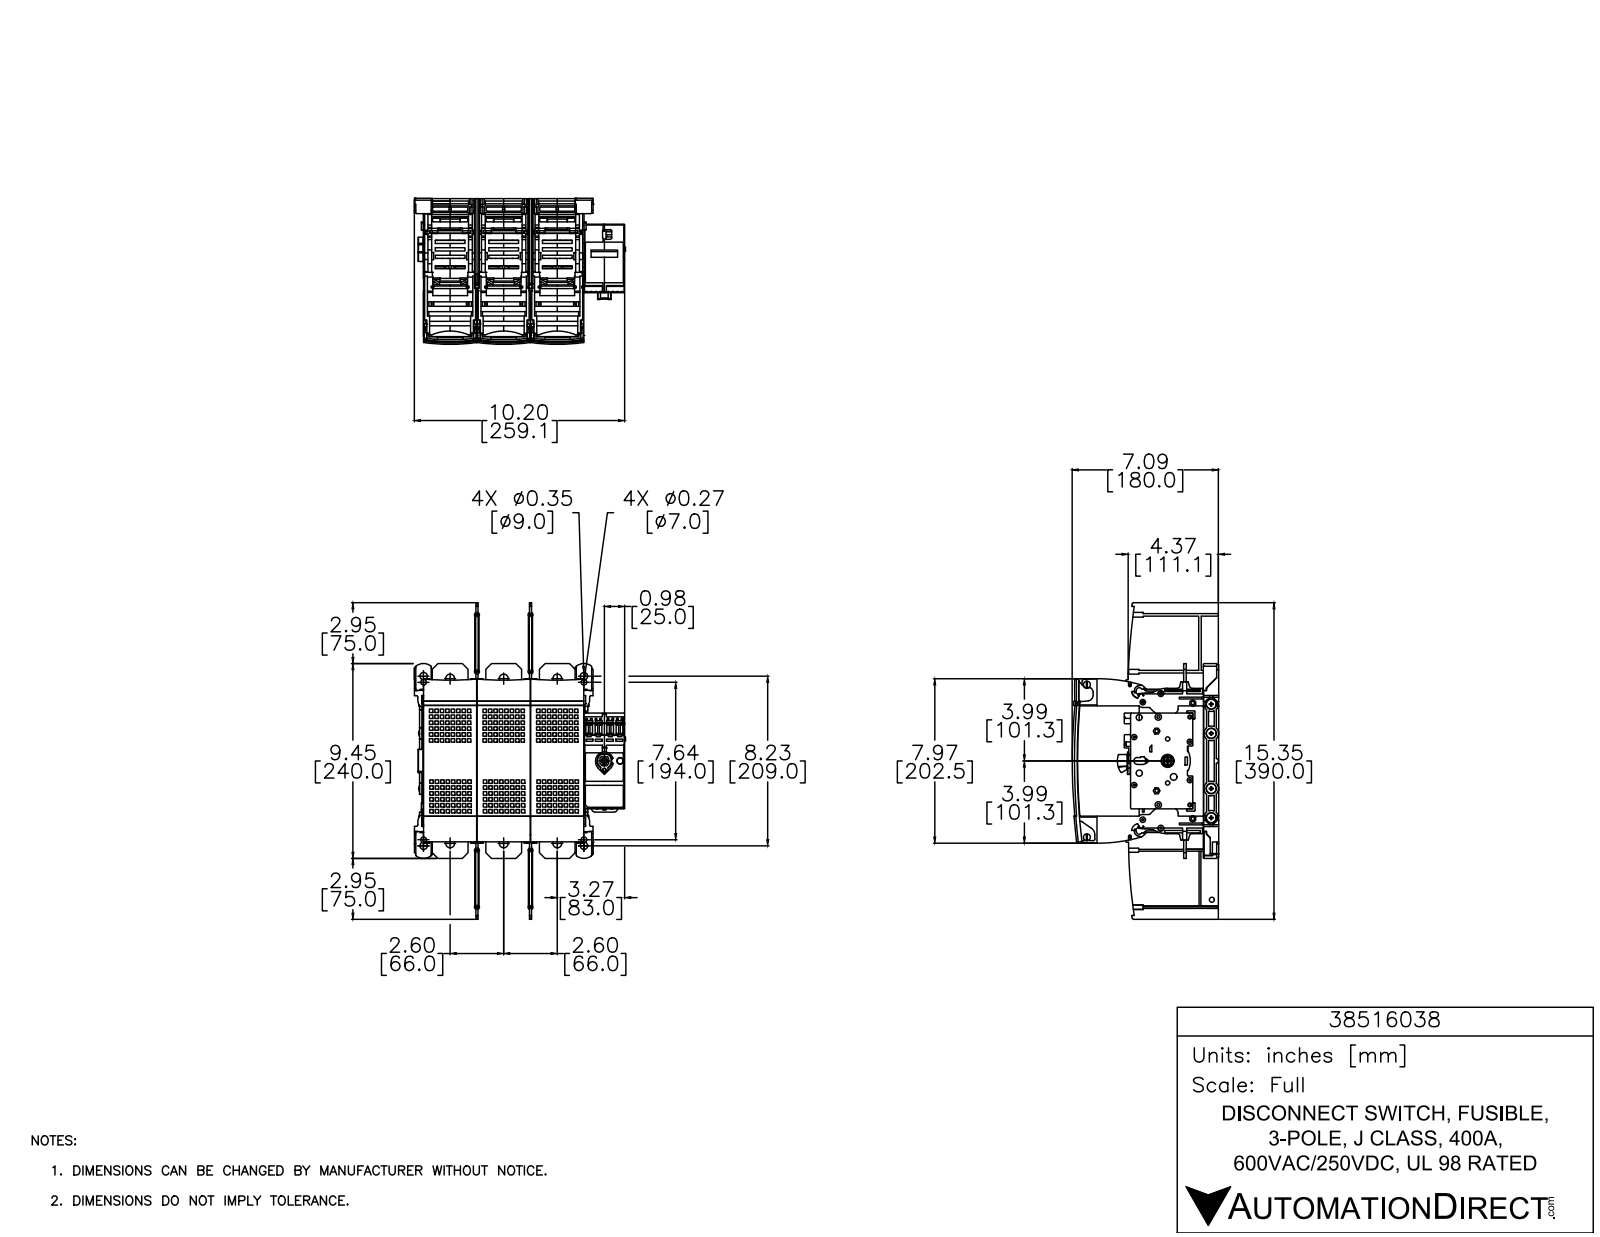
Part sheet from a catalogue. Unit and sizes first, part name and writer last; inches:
Units: inches
Overall size (bounding box): 15.354 × 10.217 × 7.087
Round holes (diameter × count): ⌀0.433 ×6, ⌀0.1 ×4, ⌀0.201 ×4, ⌀0.244 ×4, ⌀0.276 ×4, ⌀0.354 ×4, ⌀0.472 ×4, ⌀0.12 ×1, ⌀0.626 ×1, ⌀1.449 ×1
Round bosses / shafts (diameter × count): ⌀0.268 ×4, ⌀0.236 ×4, ⌀0.335 ×2, ⌀1.181 ×1
Partial cylindrical surfaces — rounded edges, fillets, slot ends (radius × count): R0.02 ×10, R0.079 ×8, R0.118 ×8, R0.512 ×8, R0.039 ×6, R0.394 ×6, R19.744 ×6, R0.045 ×4
Main face-to-face distances: 2.598, 0.11, 0.098, 2.486, 0.112, 5.148, 2.549, 2.648, 5.246, 2.474
Hole centre spacings: 0.295, 2.598, 7.815, 7.82, 7.933, 8.404, 11.136, 7.992
Volume: 399.2 in³ · Surface area: 937.1 in²
Bodies: 19 solids, 3689 faces (2774 planar, 652 cylindrical, 263 other)
Part name (STEP PRODUCT): 38513038
STEP written by: SolidWorks 2015 (AUTOMOTIVE_DESIGN)
